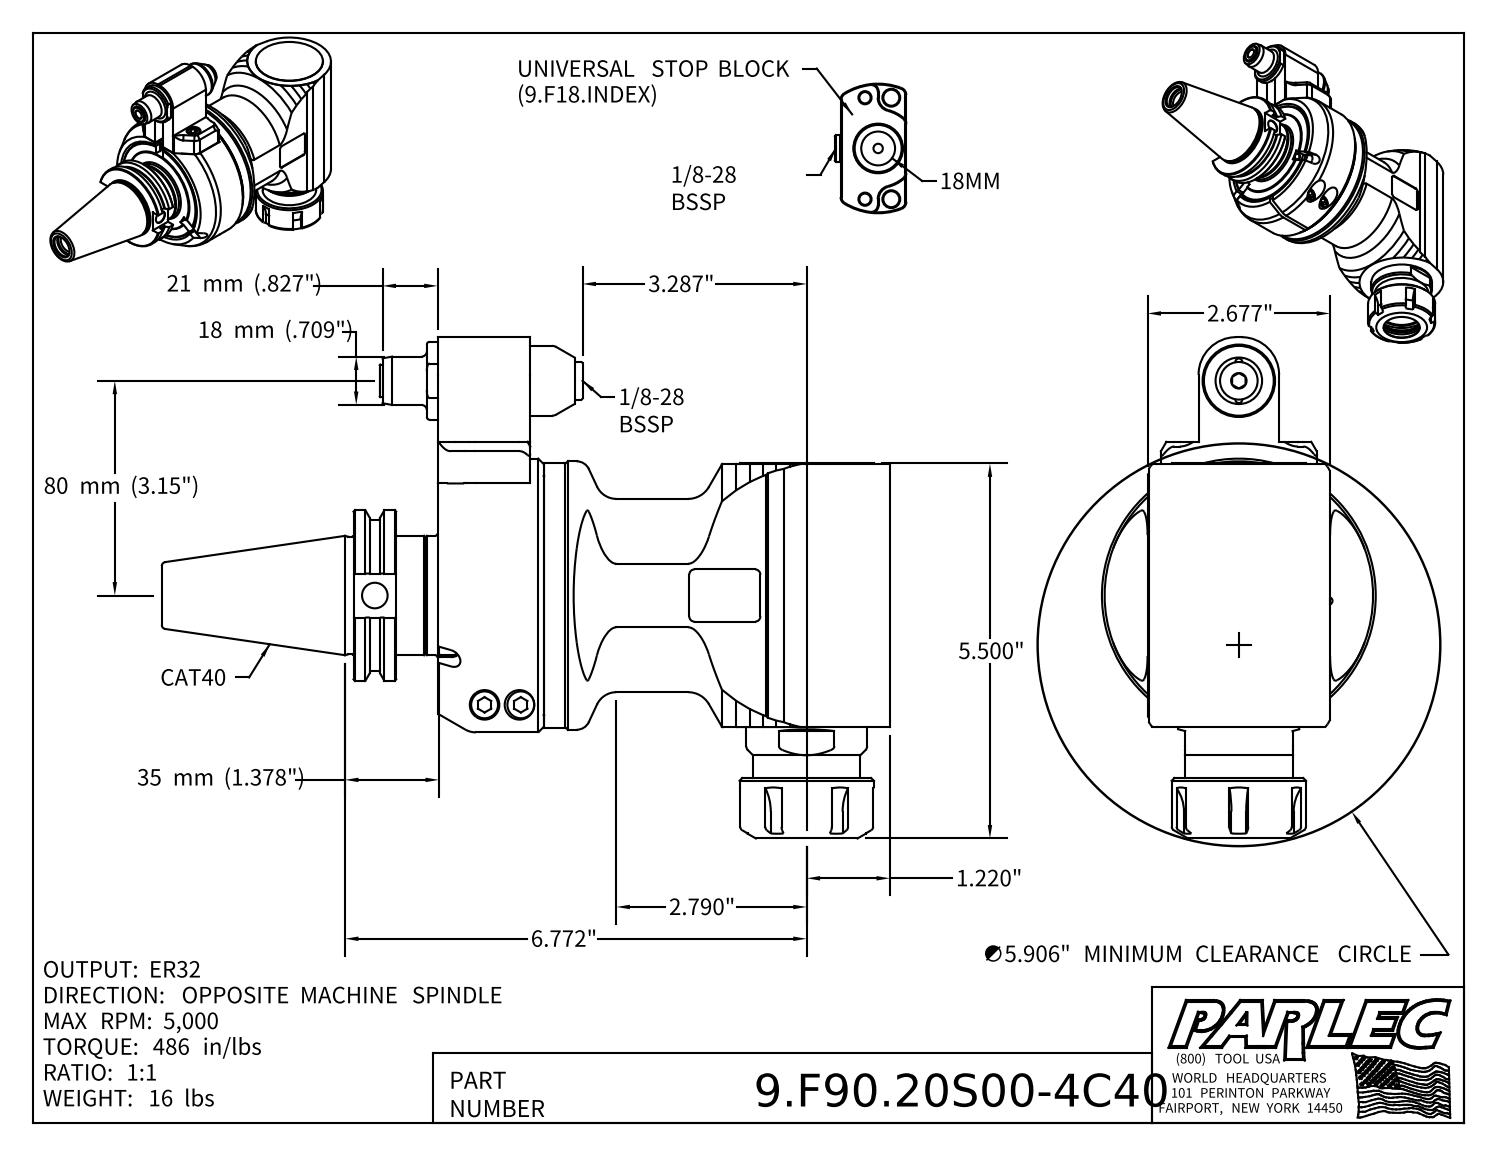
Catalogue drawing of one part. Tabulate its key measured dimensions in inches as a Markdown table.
| quantity | value |
| --- | --- |
| part name | 9.F90.20S00-4C40; 9_F90_20S00; 9_GA1_441_2 (EVO, Type 1, Cat40, 80mm) |
| STEP written by | Autodesk Inventor 2022 (AUTOMOTIVE_DESIGN) |
| units | inches |
| bodies | 8 solids, 524 faces (236 planar, 118 cylindrical, 170 other) |
| overall size | 10.679 × 7.352 × 4.016 |
| volume | 74.13 in³ |
| surface area | 256.6 in² |
| round holes (diameter × count) | 0.102 × 2, 0.165 × 2, 0.197 × 2, 0.409 × 2, 0.433 × 2, 0.492 × 2, 1.063 × 2, 0.098 × 1, 0.118 × 1, 0.256 × 1, 0.276 × 1, 0.375 × 1 |
| round bosses / shafts (diameter × count) | 0.394 × 4, 0.236 × 4, 1.575 × 2, 0.098 × 2, 4.016 × 1, 3.937 × 1, 3.874 × 1, 3.031 × 1 |
| partial cylindrical surfaces (radius × count) | 0.079 × 12, 0.591 × 6, 0.157 × 4, 0.02 × 2, 0.039 × 2, 0.138 × 2, 0.197 × 2, 0.551 × 2 |
| main face-to-face distances | 1.26, 0.02, 0.748, 0.285, 1.555, 0.276, 0.295, 1.28, 0.197, 2.677 |
| hole center spacings | 0.276, 0.512, 0.551, 1.72, 2.272, 2.659, 2.874, 3.15 |
